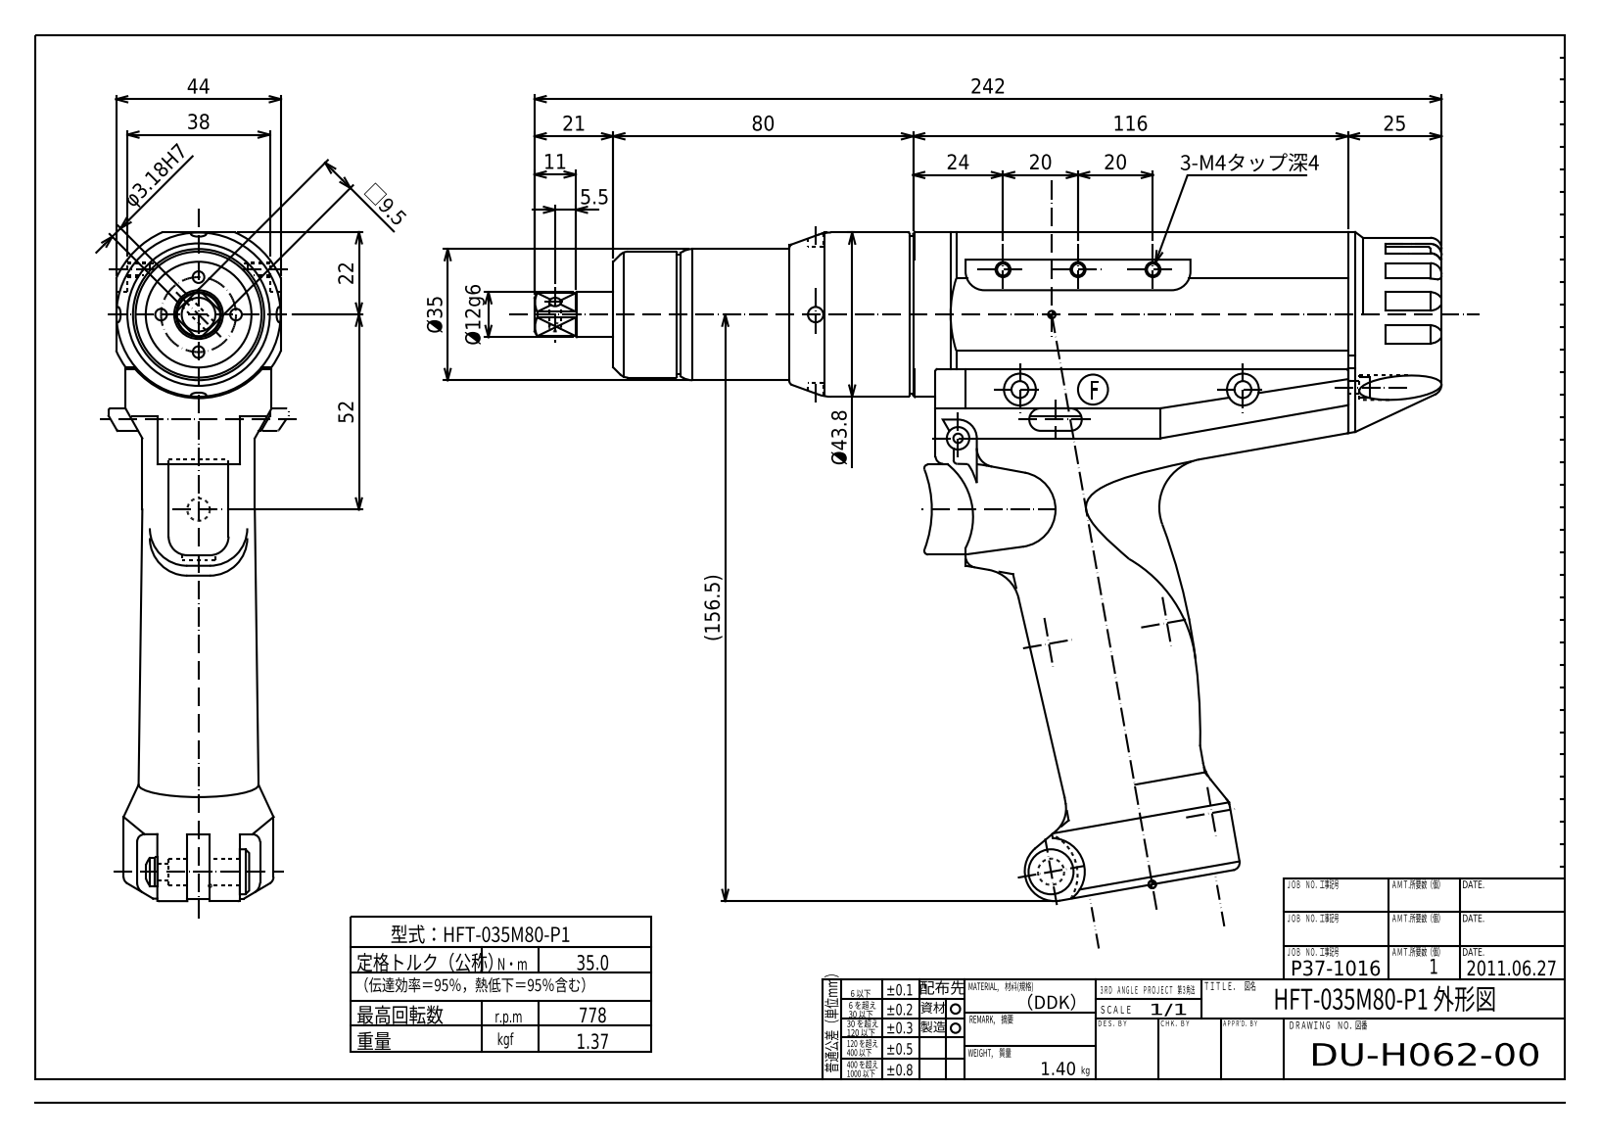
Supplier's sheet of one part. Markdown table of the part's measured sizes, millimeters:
| quantity | value |
| --- | --- |
| part name | HFT-035M80-P1(DU-H062+L)_OUTLINE |
| STEP written by | Autodesk Inventor 2023 (CONFIG_CONTROL_DESIGN) |
| units | millimeters |
| bodies | 1 solid, 1241 faces (566 planar, 265 cylindrical, 410 other) |
| overall size | 242 × 178.46 × 46 |
| volume | 502 270 mm³ |
| surface area | 92 336 mm² |
| round holes (diameter × count) | 3.24 × 8, 3.1 × 4, 4.1 × 4, 6 × 4, 1 × 2, 2.46 × 2, 6.5 × 2, 8.5 × 2, 25 × 2, 2.5 × 1, 3.18 × 1, 3.4 × 1 |
| round bosses / shafts (diameter × count) | 1 × 24, 1.6 × 4, 5.8 × 3, 5.5 × 3, 30 × 2, 12 × 2, 8 × 2, 44 × 1 |
| partial cylindrical surfaces (radius × count) | 0.5 × 10, 1 × 8, 5 × 8, 2 × 4, 3 × 3, 4.5 × 3, 1.62 × 2, 2.1 × 2 |
| main face-to-face distances | 3, 44, 2.5, 0.5, 41.5, 3.5, 38, 9.5, 21.7, 22.3 |
| hole center spacings | 20, 10, 14.14, 40, 4.26, 6.85, 10.01, 13.92 |
